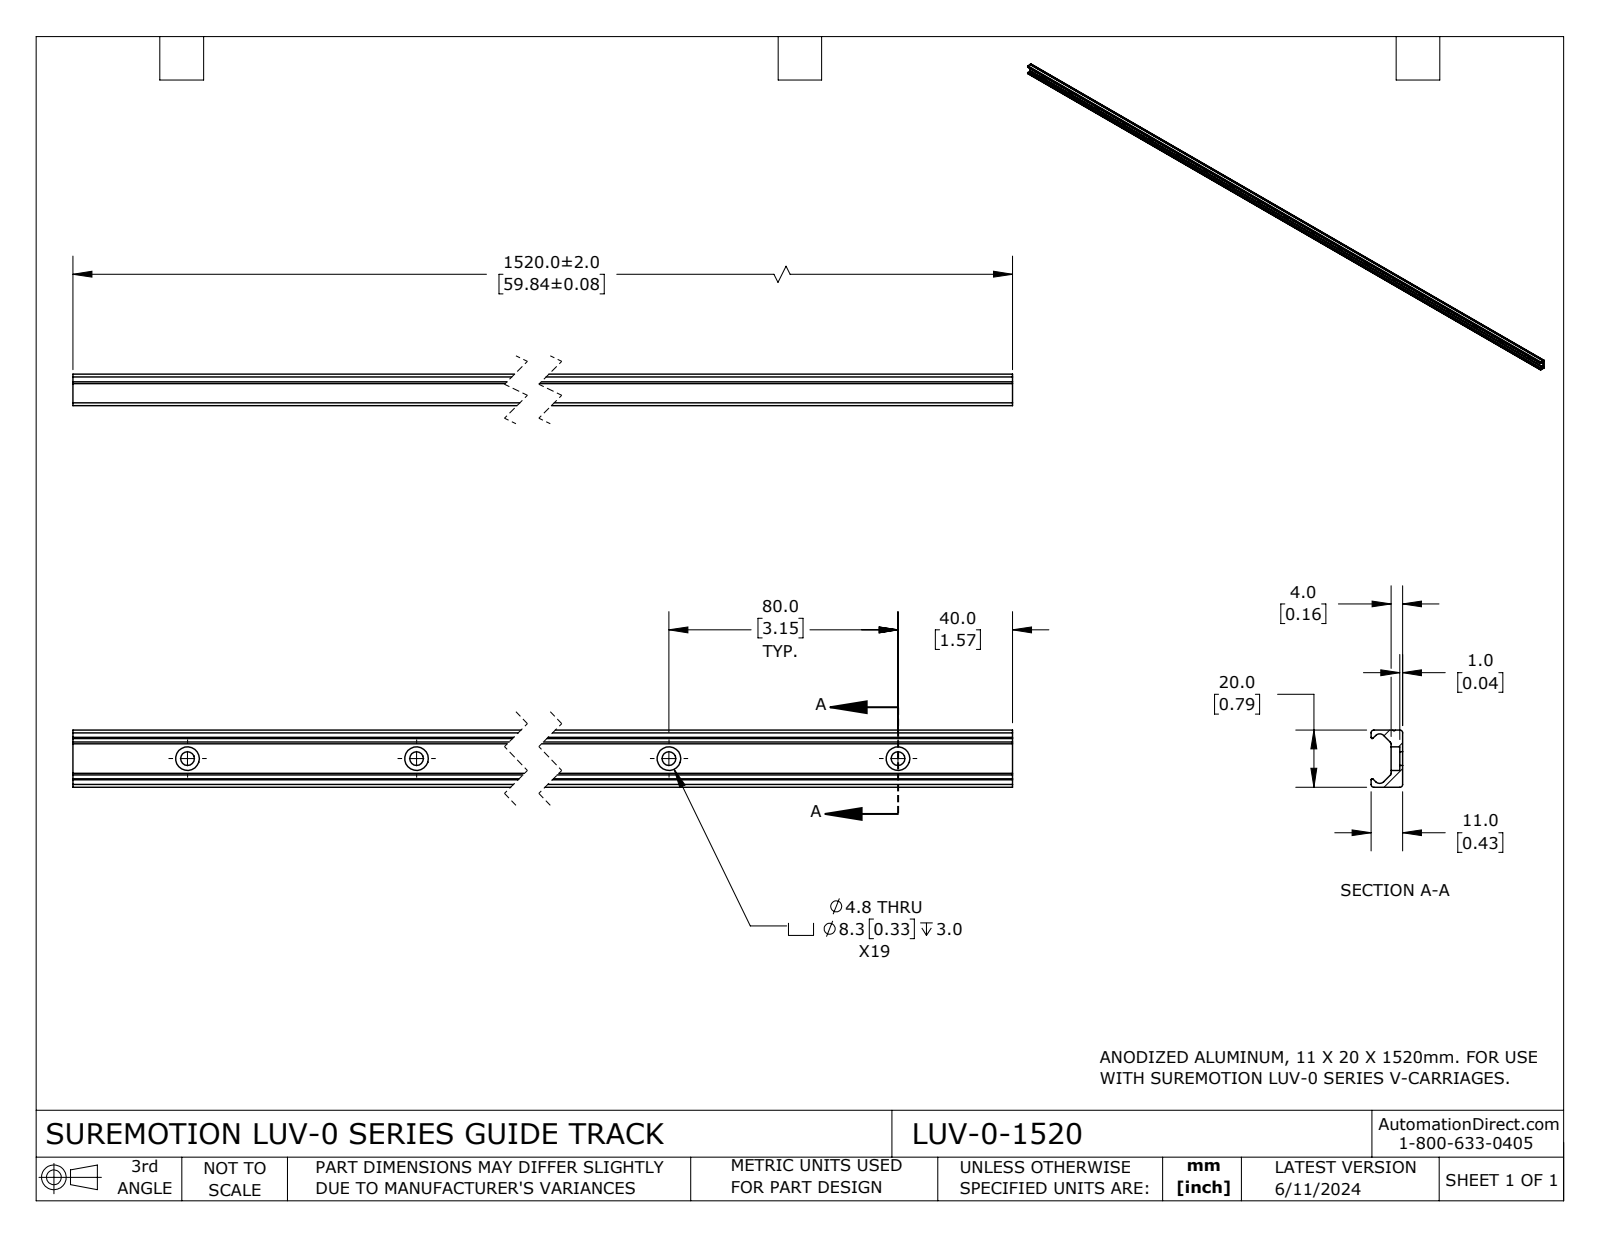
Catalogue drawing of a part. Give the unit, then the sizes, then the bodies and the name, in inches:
Units: inches
Overall size (bounding box): 59.843 × 0.787 × 0.433
Round holes (diameter × count): ⌀0.189 ×19, ⌀0.325 ×12, ⌀0.325 ×7
Partial cylindrical surfaces — rounded edges, fillets, slot ends (radius × count): R0.039 ×4, R0.015 ×2, R0.016 ×2, R0.031 ×2, R0.078 ×2, R0.013 ×1
Main face-to-face distances: 0.158, 0.787, 0.433, 0.275, 0.528, 0.04, 0.118, 0.393, 59.843
Hole centre spacings: 3.15, 6.299, 9.449, 12.598, 15.748, 18.898, 22.047, 25.197
Volume: 10.24 in³ · Surface area: 178.2 in²
Bodies: 1 solid, 121 faces (32 planar, 89 cylindrical, 0 other)
Part name (STEP PRODUCT): LUV-0-1520
STEP written by: SolidWorks 2023 (CONFIG_CONTROL_DESIGN)
